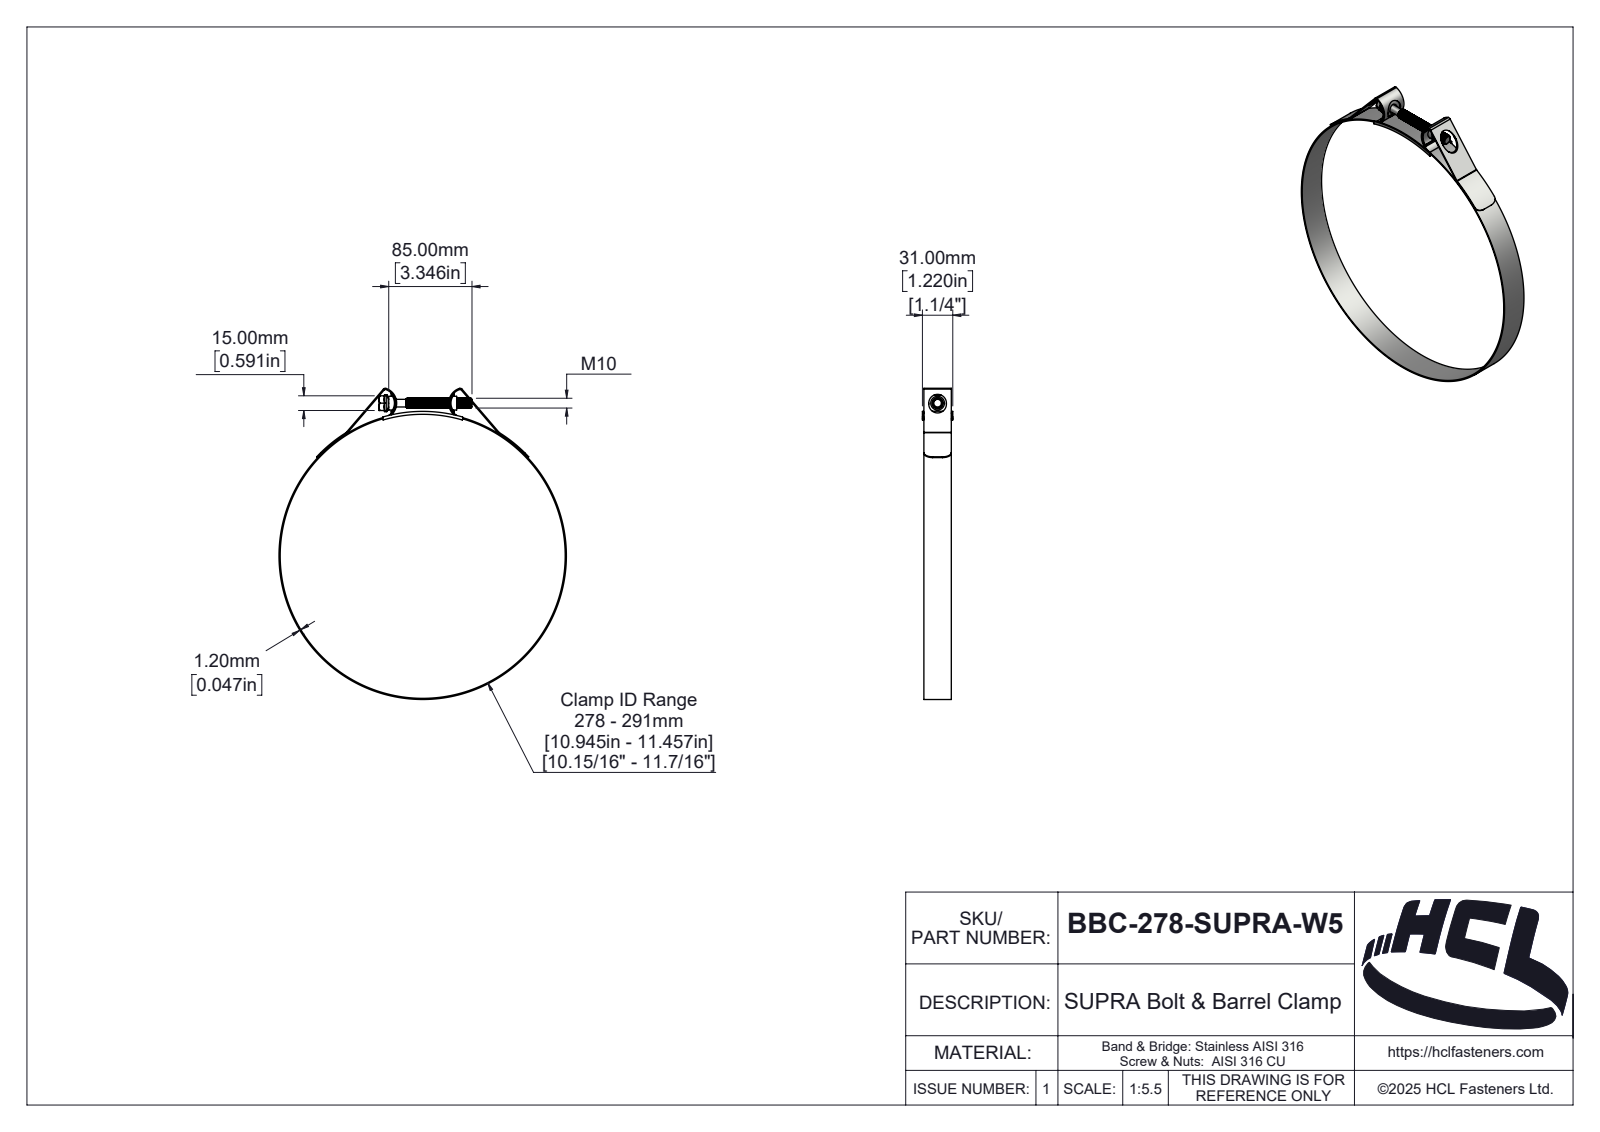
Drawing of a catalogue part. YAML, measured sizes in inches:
part_name: "BBC-278-SUPRA-W5"
step_written_by: "SolidWorks 2025 (AUTOMOTIVE_DESIGN)"
units: inches
bodies: {solids: 5, faces: 381, planar: 50, cylindrical: 244, other: 87}
overall_size: [12.503, 11.551, 1.22]
volume: 2.972
surface_area: 118.8
round_holes:
  - {diameter: 11.457, count: 1}
round_bosses_or_shafts:
  - {diameter: 11.551, count: 1}
  - {diameter: 0.682, count: 1}
  - {diameter: 0.551, count: 1}
  - {diameter: 0.394, count: 1}
  - {diameter: 0.307, count: 1}
partial_cylinders:
  - {radius: 0.039, count: 4}
  - {radius: 0.051, count: 2}
  - {radius: 0.079, count: 2}
  - {radius: 0.098, count: 2}
  - {radius: 0.126, count: 2}
  - {radius: 0.354, count: 2}
  - {radius: 0.534, count: 2}
  - {radius: 0.573, count: 2}
face_to_face_distances: [0.047, 1.102, 0.059, 1.161, 1.173, 1.114, 1.22, 1.126, 0.591, 0.098]
